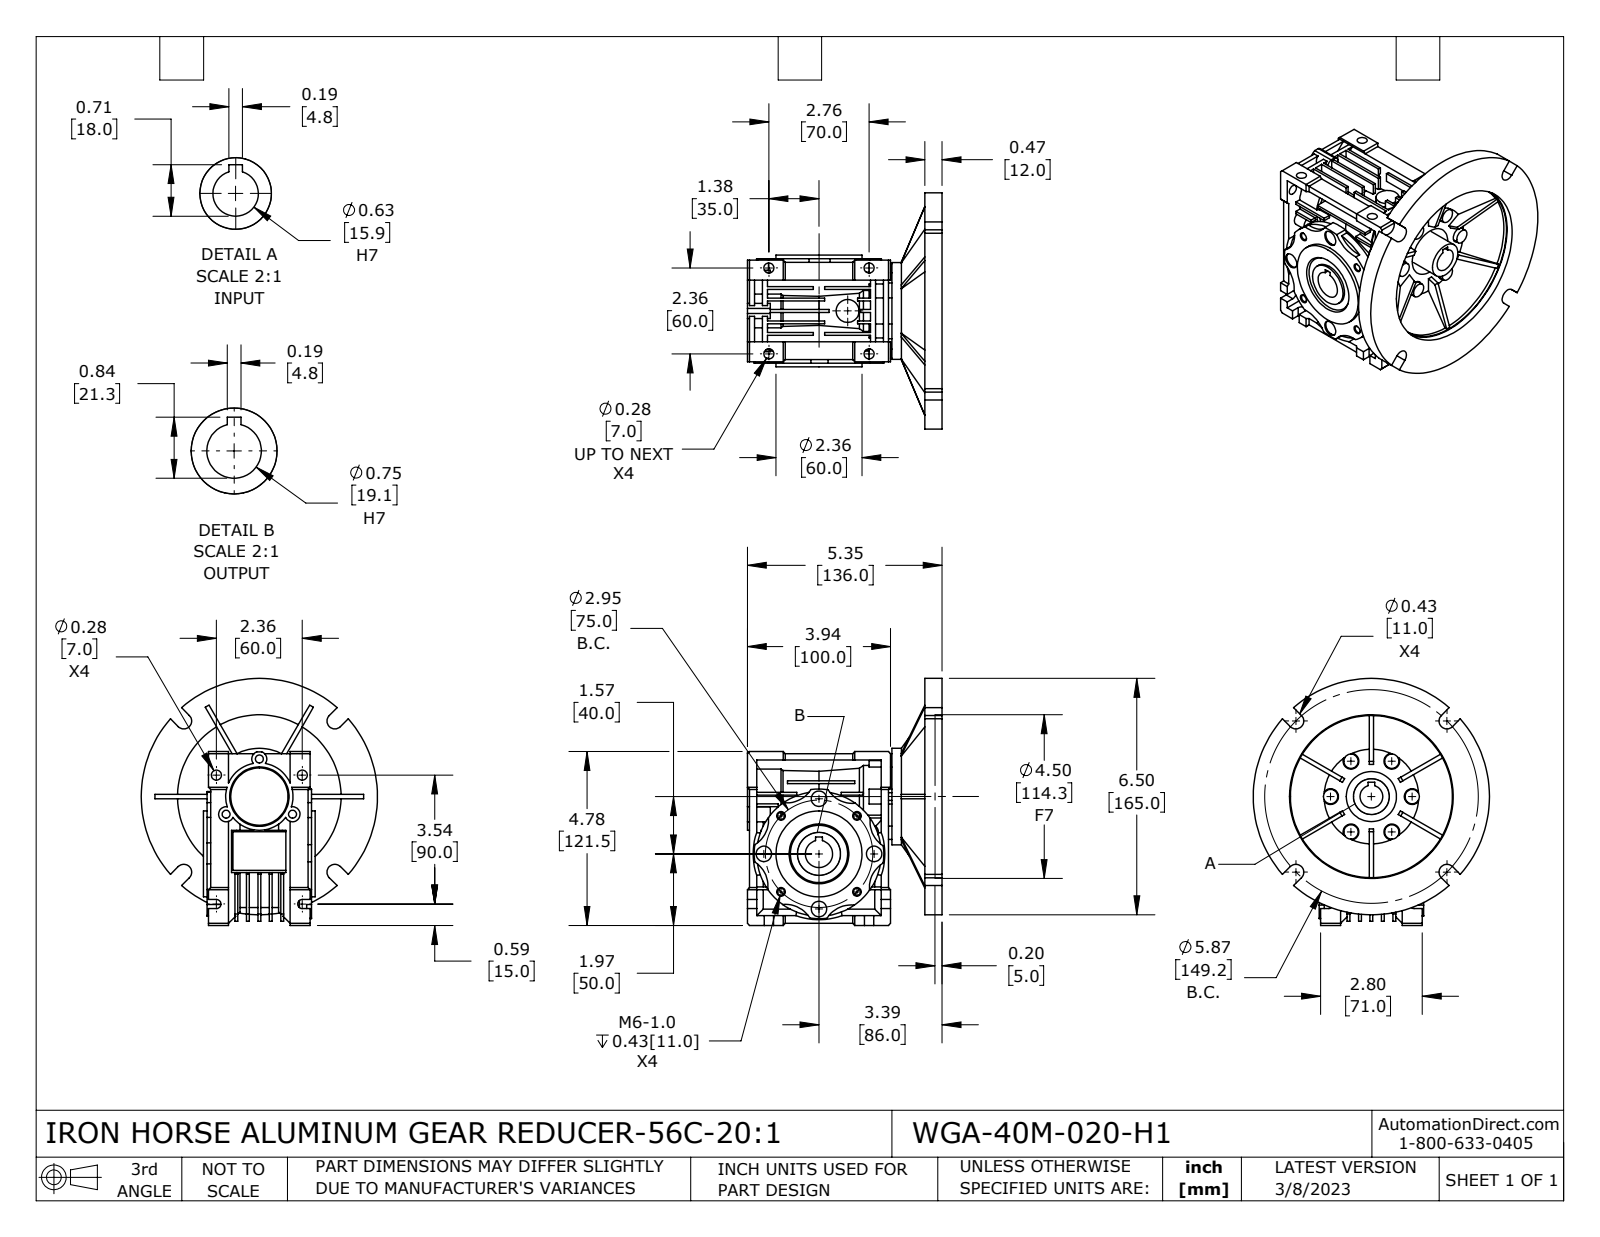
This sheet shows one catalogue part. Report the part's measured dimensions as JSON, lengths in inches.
{"part_name": "WGA-40M-020-H1", "step_written_by": "SolidWorks 2021 (CONFIG_CONTROL_DESIGN)", "units": "inches", "bodies": {"solids": 4, "faces": 856, "planar": 511, "cylindrical": 251, "other": 94}, "overall_size": [6.791, 6.496, 5.354], "volume_in3": 50.34, "surface_area_in2": 315, "round_holes": [[0.276, 6], [0.433, 6], [0.194, 4], [0.425, 4], [0.219, 3], [0.625, 1], [0.65, 1], [0.75, 1], [0.906, 1], [1.102, 1], [1.181, 1], [1.378, 1]], "round_bosses_or_shafts": [[0.394, 6], [6.496, 1], [2.953, 1], [2.657, 1], [2.362, 1], [2.126, 1], [1.85, 1], [1.417, 1]], "partial_cylinders_radius": [[0.787, 8], [0.126, 6], [0.206, 6], [0.217, 4], [0.207, 3], [1.713, 1], [1.716, 1], [1.781, 1]], "face_to_face_distances": [0.315, 0.472, 0.079, 0.945, 0.236, 0.059, 0.63, 0.098, 0.394, 0.197], "hole_center_spacings": [1.122, 1.146, 2.765, 1.943, 1.476, 1.516, 2.088, 2.144]}
